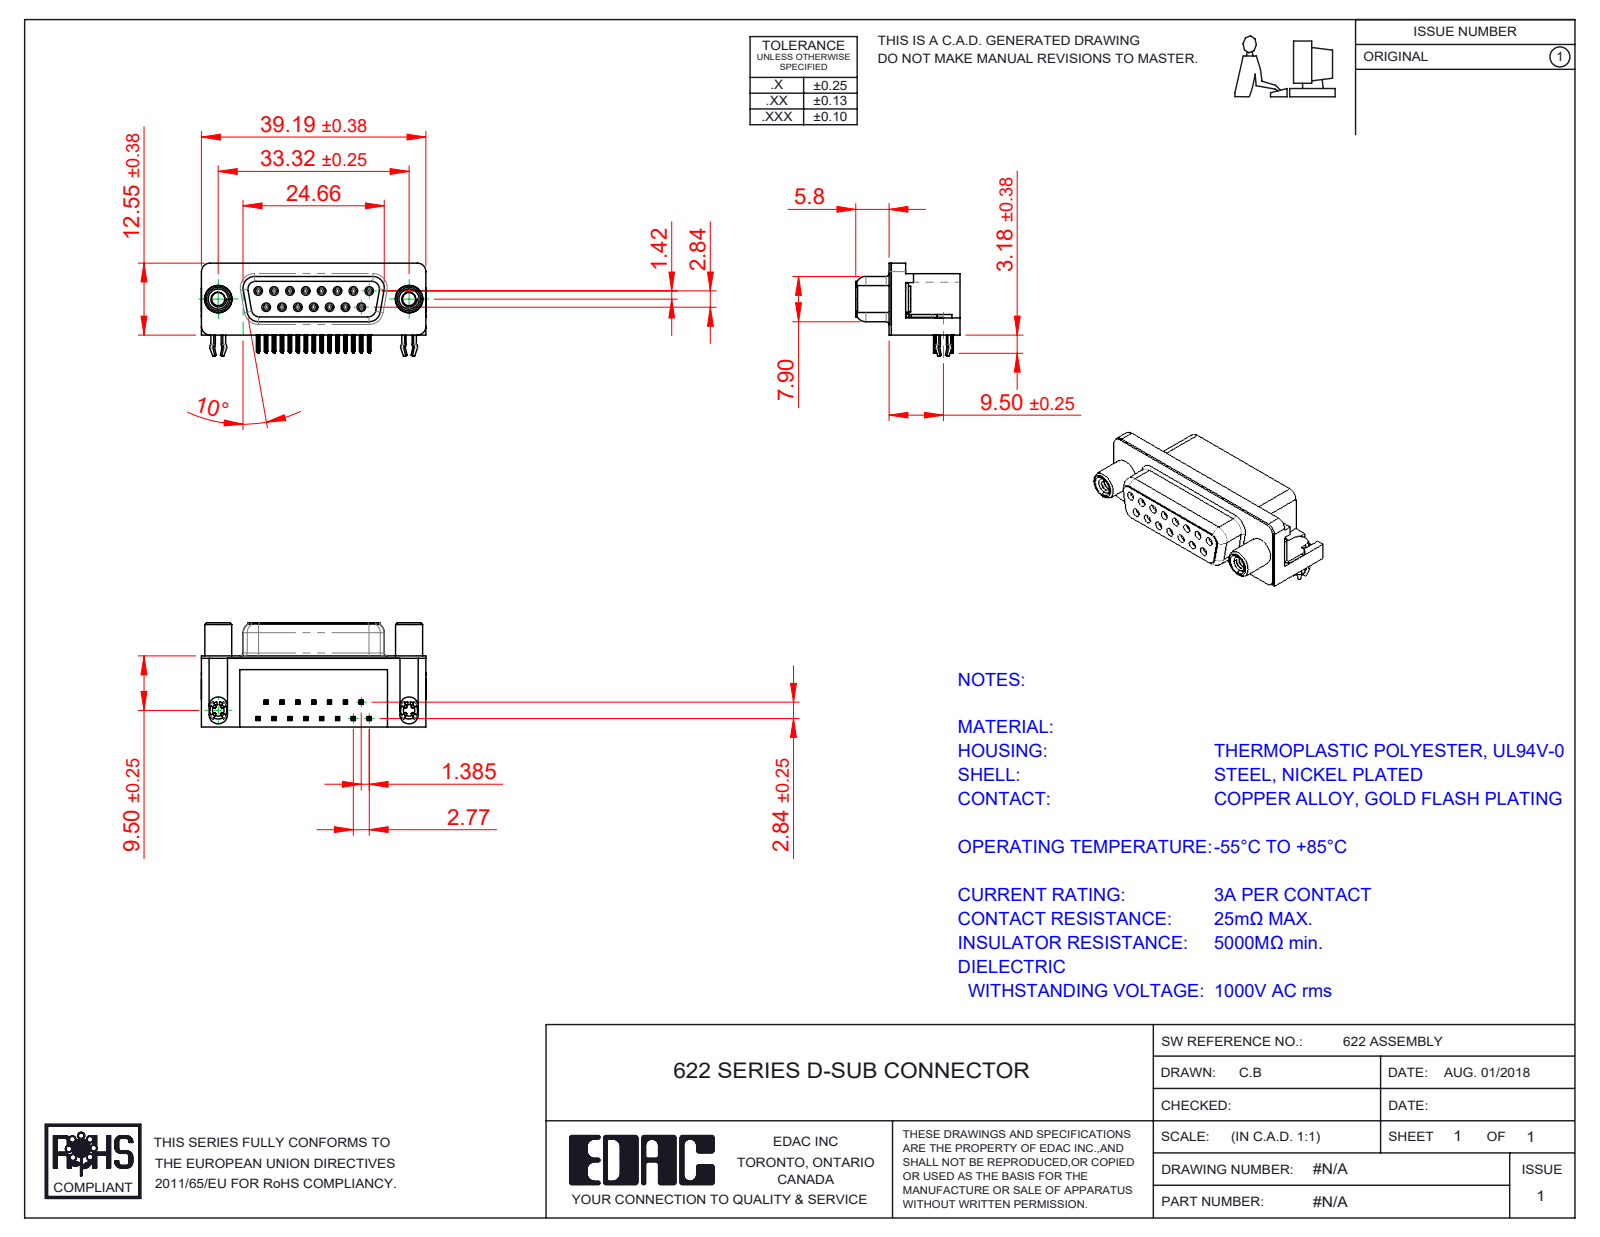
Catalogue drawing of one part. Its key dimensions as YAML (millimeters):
part_name: "622 Round Threaded Standoff; 622 4-40 Threaded Board Mount; 622 Socket Bottom; 622 Contact Top (+3 more)"
step_written_by: "SolidWorks 2016 (CONFIG_CONTROL_DESIGN)"
units: millimeters
bodies: {solids: 21, faces: 2451, planar: 1066, cylindrical: 625, other: 760}
overall_size: [39.22, 18.2, 15.73]
volume: 5290
surface_area: 6994
round_holes:
  - {diameter: 0.8, count: 15}
  - {diameter: 0.9, count: 15}
  - {diameter: 2.26, count: 2}
  - {diameter: 2.3, count: 2}
  - {diameter: 3.1, count: 2}
  - {diameter: 4, count: 2}
  - {diameter: 4.8, count: 2}
  - {diameter: 5, count: 2}
round_bosses_or_shafts:
  - {diameter: 1.2, count: 15}
  - {diameter: 4.9, count: 2}
  - {diameter: 4.7, count: 2}
  - {diameter: 4.5, count: 2}
  - {diameter: 3.85, count: 2}
  - {diameter: 3.26, count: 2}
partial_cylinders:
  - {radius: 0.1, count: 120}
  - {radius: 0.15, count: 60}
  - {radius: 0.35, count: 30}
  - {radius: 1, count: 18}
  - {radius: 0.34, count: 15}
  - {radius: 1.35, count: 8}
  - {radius: 1.5, count: 8}
  - {radius: 1.6, count: 8}
face_to_face_distances: [0.4, 12, 6.2, 10.35, 12.4, 2.9, 6.65, 0.85, 0.35, 5.8]
hole_center_spacings: [3.16, 2.77, 5.54, 8.31, 11.08, 5.03, 5.04, 7.48]
